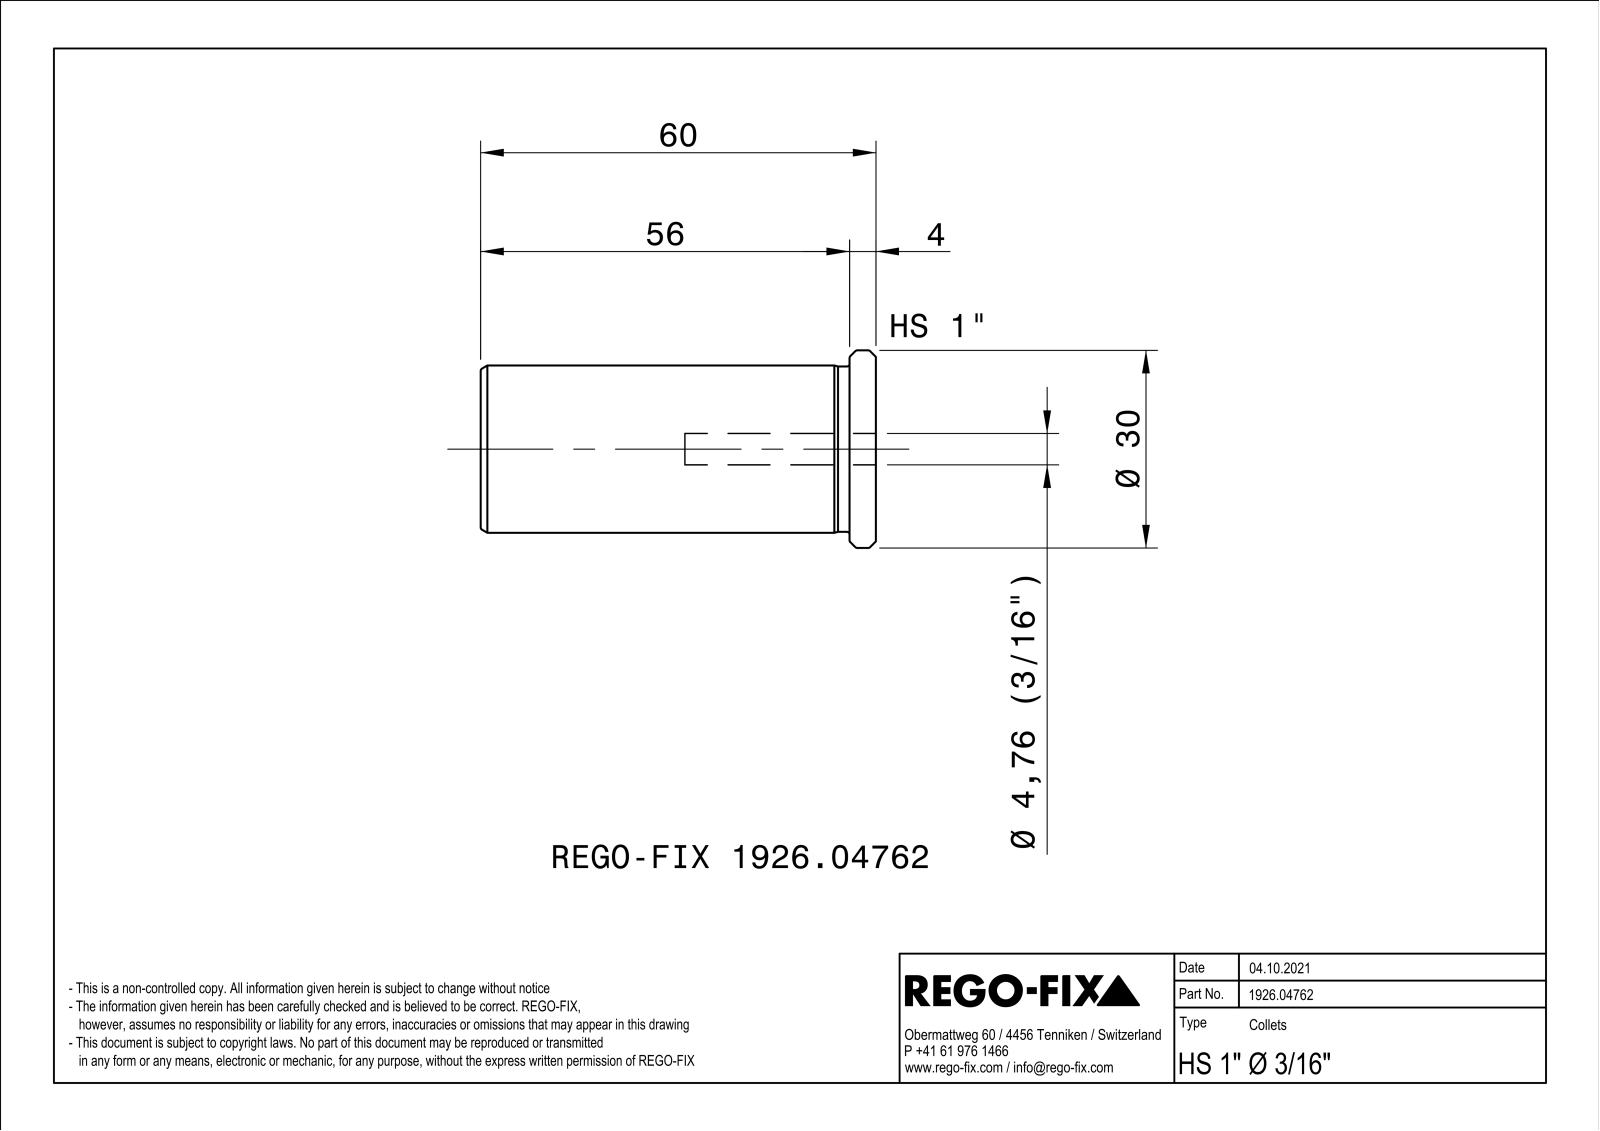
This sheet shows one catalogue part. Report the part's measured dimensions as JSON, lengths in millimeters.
{"part_name": "NOCUT", "step_written_by": "SIEMENS PLM Software Solid Edge ST10 (AUTOMOTIVE_DESIGN)", "units": "millimeters", "bodies": {"solids": 1, "faces": 72, "planar": 22, "cylindrical": 12, "other": 38}, "overall_size": [60, 29.98, 29.98], "volume_mm3": 23958, "surface_area_mm2": 10046, "round_holes": [[4.76, 1], [10, 1], [20.5, 1]], "round_bosses_or_shafts": [[30, 1], [25.4, 1], [25.1, 1]], "face_to_face_distances": [1, 60, 4, 56]}
